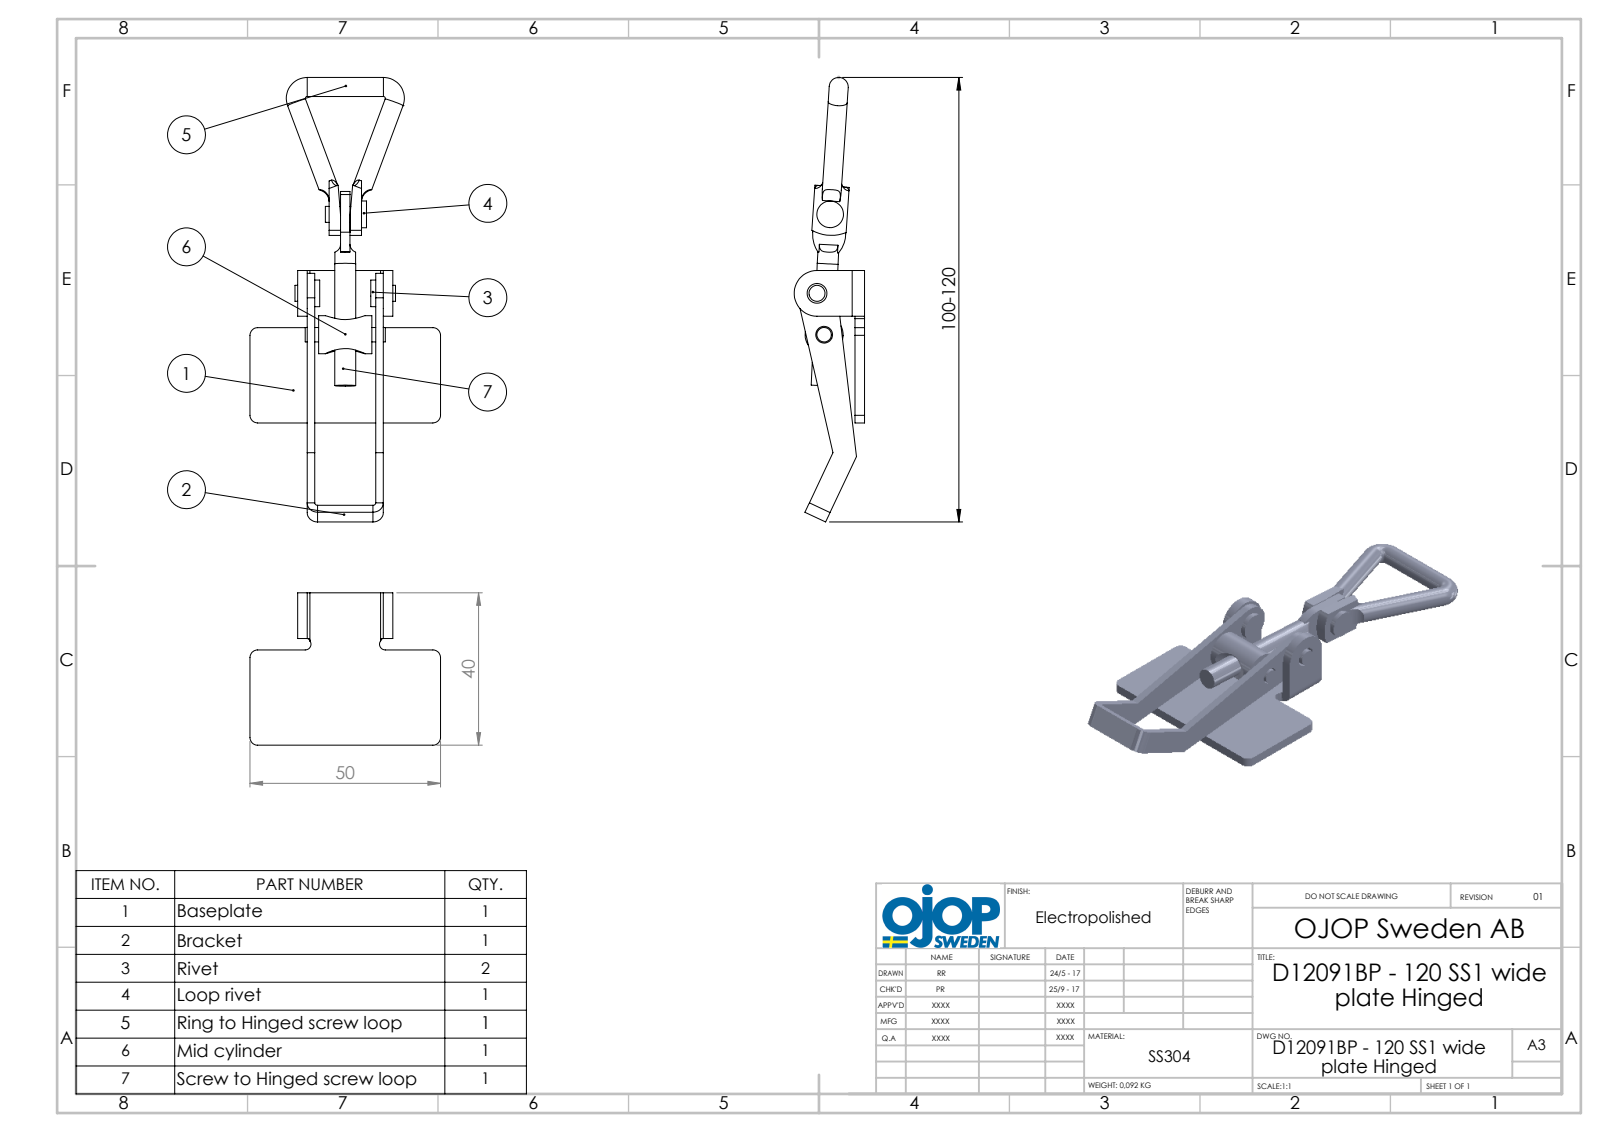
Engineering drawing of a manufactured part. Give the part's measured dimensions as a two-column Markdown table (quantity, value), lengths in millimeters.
| quantity | value |
| --- | --- |
| part name | bygel; ring till ledad öggla; Platta; nitöggla (+4 more) |
| STEP written by | SolidWorks 2015 (AUTOMOTIVE_DESIGN) |
| units | millimeters |
| bodies | 8 solids, 175 faces (77 planar, 78 cylindrical, 20 other) |
| overall size | 116.64 × 50 × 18.47 |
| volume | 11 349 mm³ |
| surface area | 11 504 mm² |
| round holes (diameter × count) | 4.4 × 1, 4.5 × 1, 5.2 × 1, 5.5 × 1 |
| round bosses / shafts (diameter × count) | 5 × 3, 7 × 2, 4.2 × 2, 10 × 1, 5.47 × 1, 5.46 × 1, 3.8 × 1 |
| partial cylindrical surfaces (radius × count) | 2 × 6, 0.74 × 4, 1.5 × 2, 2.74 × 2, 3 × 2, 3.24 × 2, 10 × 2, 5.25 × 1 |
| main face-to-face distances | 2.5, 18, 2, 20, 16, 3, 15, 4.5, 20.5, 22.5 |
| hole center spacings | 11.02, 21.01, 31.62 |
